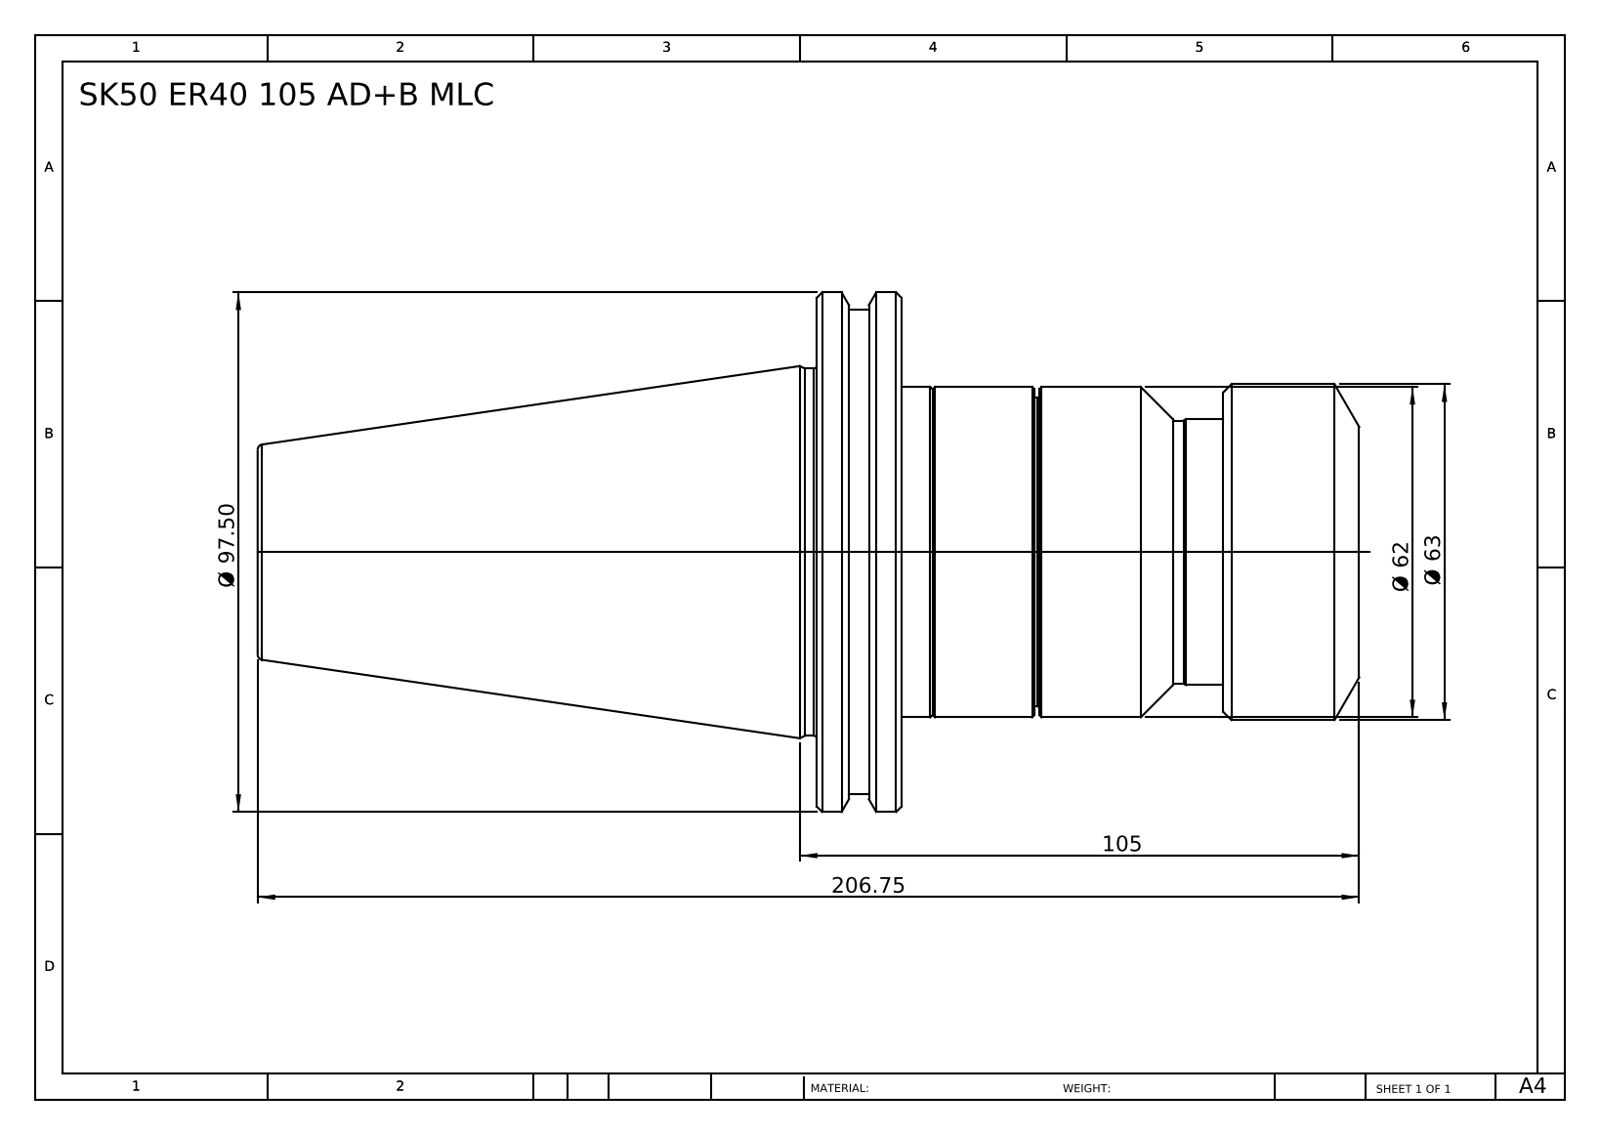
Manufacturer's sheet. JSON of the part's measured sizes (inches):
{"part_name": "SK 50 ER 40 105 AD+B MLC", "step_written_by": "SolidWorks 2014 (CONFIG_CONTROL_DESIGN)", "units": "inches", "bodies": {"solids": 1, "faces": 67, "planar": 11, "cylindrical": 22, "other": 34}, "overall_size": [8.14, 3.839, 3.839], "volume_in3": 37.71, "surface_area_in2": 84.52, "round_bosses_or_shafts": [[3.839, 1], [3.583, 1], [2.717, 1], [2.48, 1], [2.441, 1], [2.28, 1], [1.965, 1], [1.945, 1]], "face_to_face_distances": [0.626, 3.382, 4.008, 8.14, 4.758, 4.132, 1.004, 2.378, 3.004, 7.136]}
